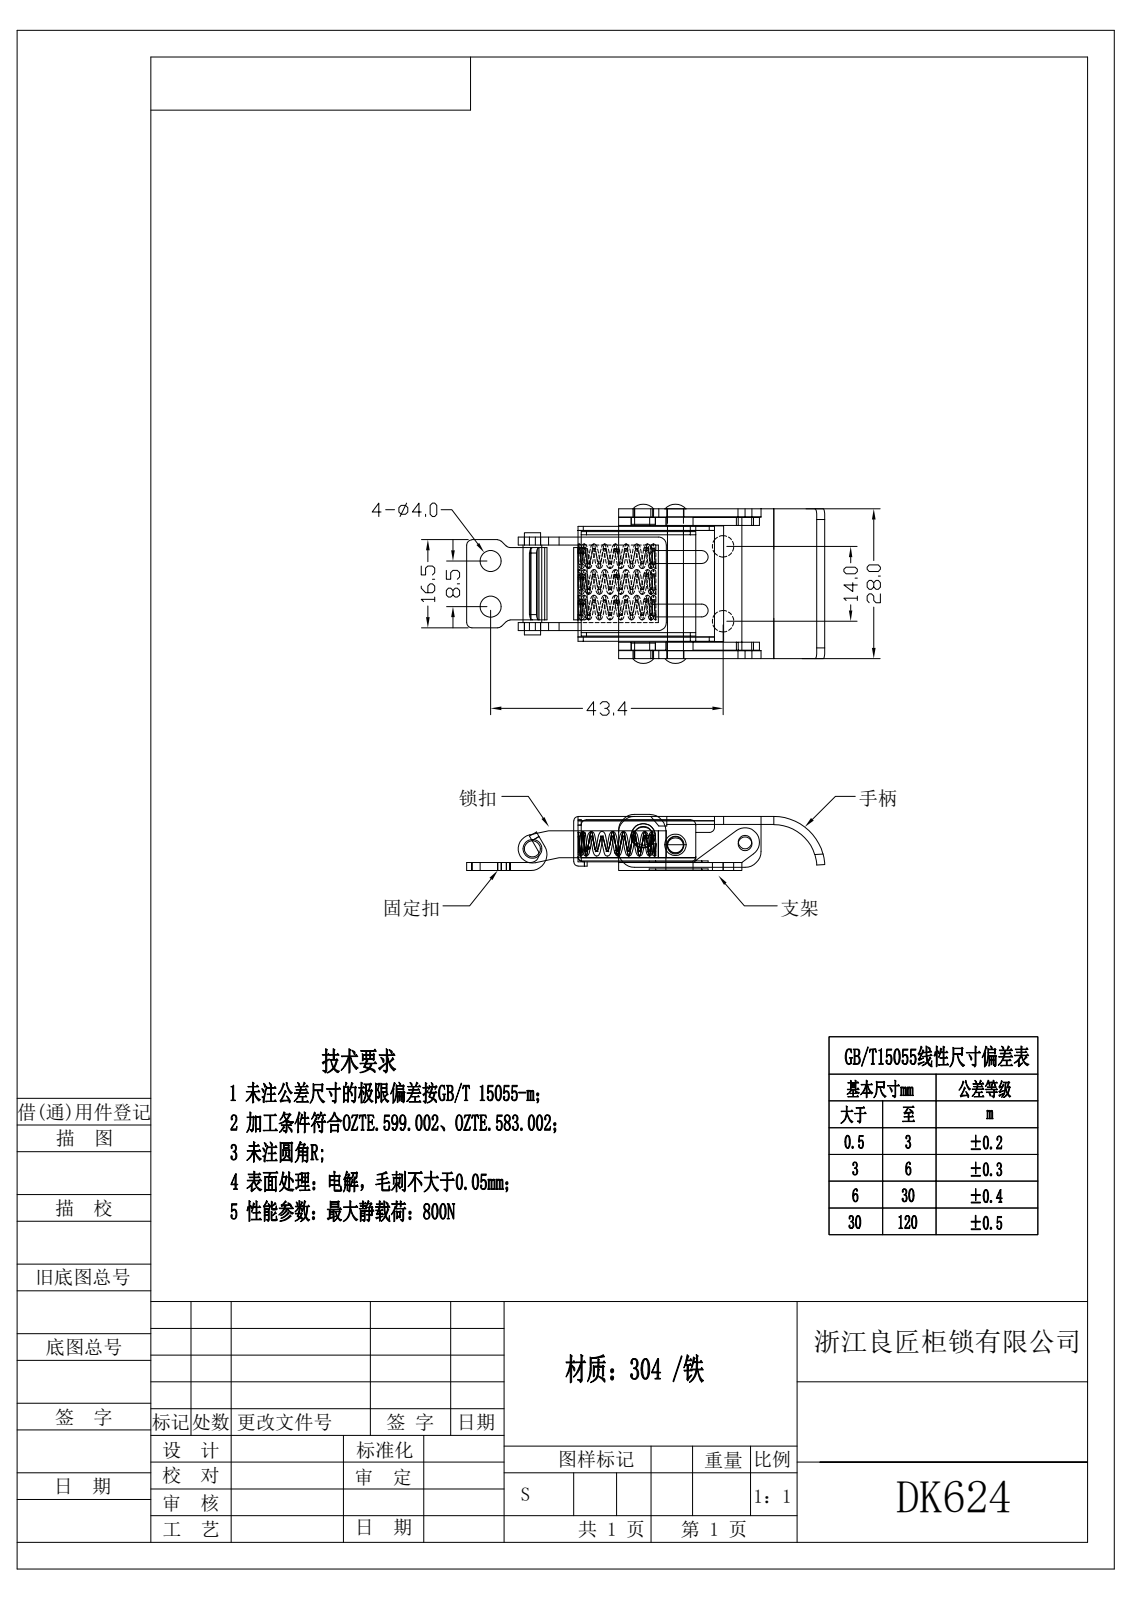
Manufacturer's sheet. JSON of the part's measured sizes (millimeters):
{"step_written_by": "Rhino 8.5 (CONFIG_CONTROL_DESIGN)", "units": "millimeters", "bodies": {"solids": 10, "faces": 324, "planar": 164, "cylindrical": 129, "other": 31}, "overall_size": [68, 31.16, 10.5], "volume_mm3": 5514, "surface_area_mm2": 11564, "round_holes": [[4, 4], [3, 3], [2.5, 1], [3.5, 1], [4.5, 1]], "round_bosses_or_shafts": [[4, 2], [3, 2], [3.5, 1], [2.3, 1]], "partial_cylinders_radius": [[1, 17], [0.2, 8], [2, 5], [0.1, 4], [0.8, 4], [0.6, 3], [3, 3], [1.12, 2]], "face_to_face_distances": [1.5, 0.8, 0.6, 8.79, 7.99, 9.49, 10.29, 1.65, 25.15, 19.9], "hole_center_spacings": [6.24, 6.46, 8.5, 13.01, 14, 19.04, 19.27, 21.24]}
